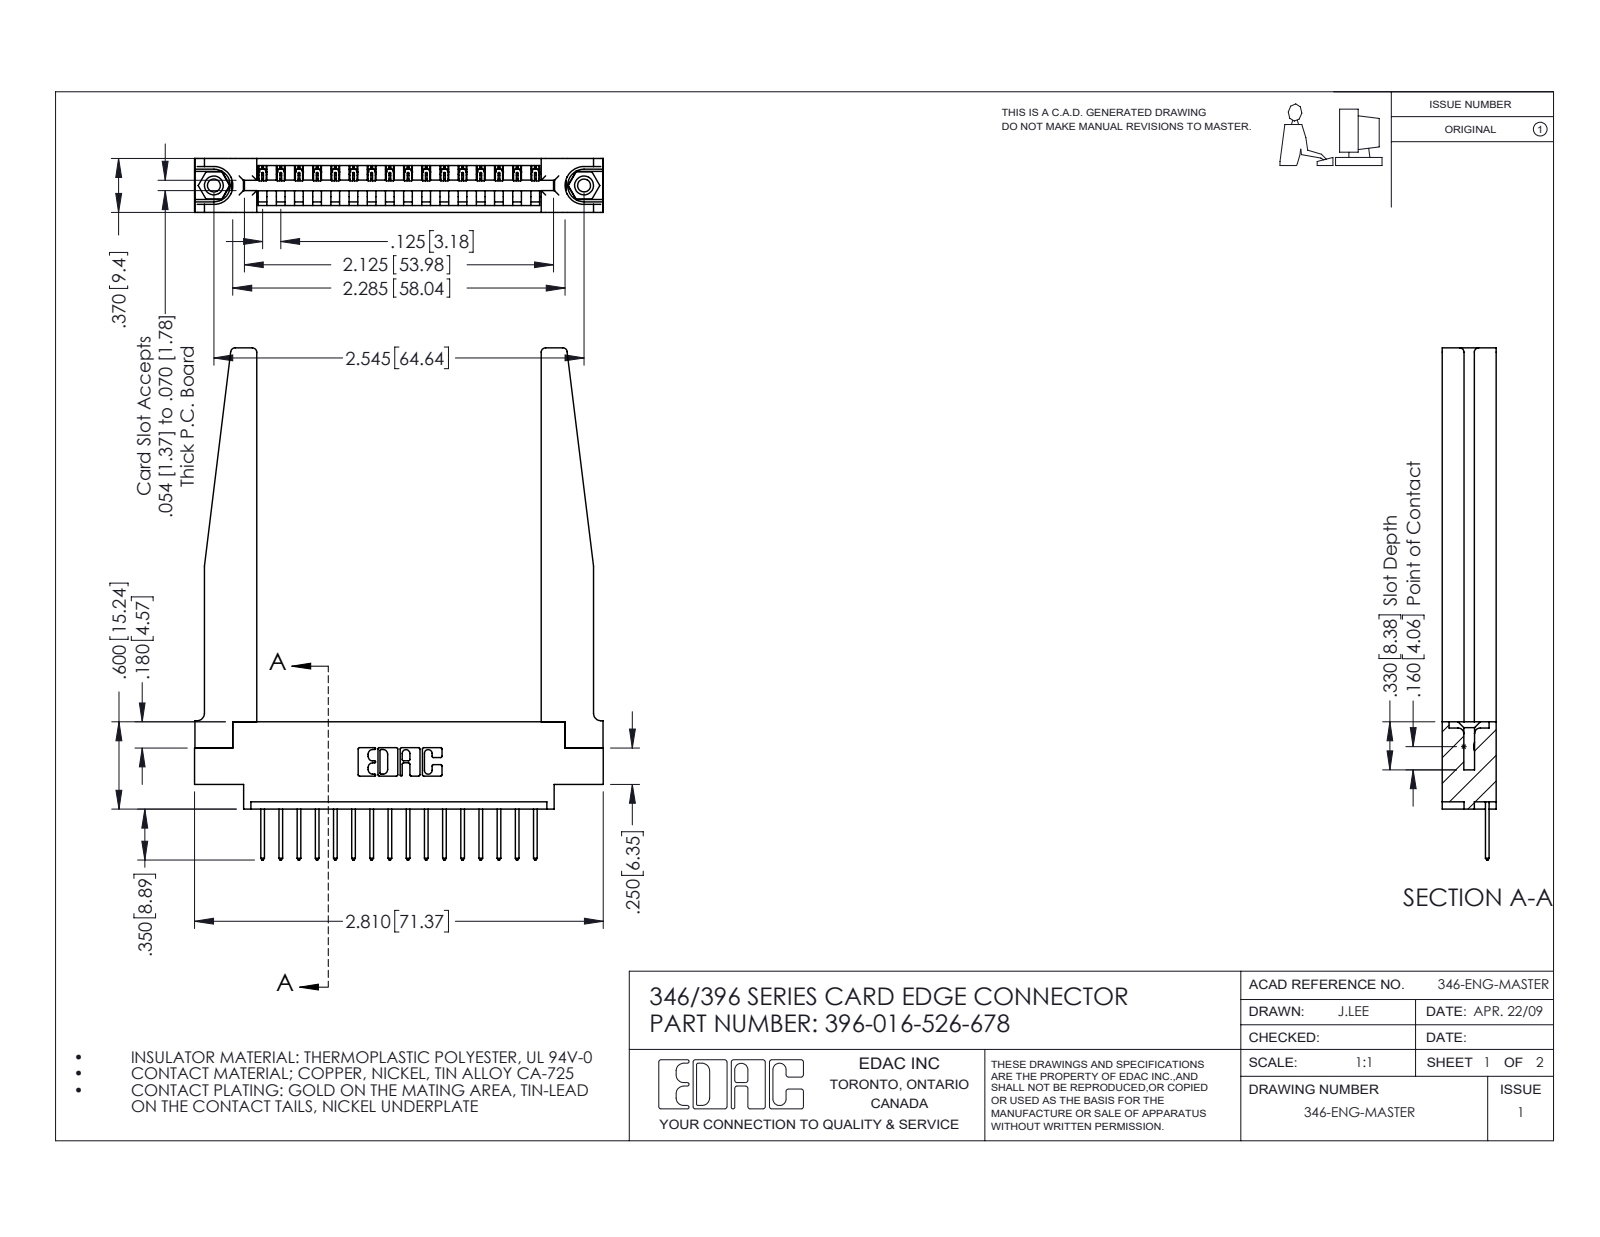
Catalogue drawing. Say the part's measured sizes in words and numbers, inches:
The part is named "345-292-001_345-293-126; 345-250-001_345-250-001-102; 346 Part_0.170 Offset - 0.156 Dia-TH; 346-220-078_345-220-078 (+1 more)". Its 3-D file was written by "SolidWorks 2016 (CONFIG_CONTROL_DESIGN)". It is 21 solids with 1288 faces: 862 planar, 374 cylindrical and 52 other. Overall it measures 3.52 by 2.81 by 0.37 inches. Its volume is 0.817 cubic inches and its surface area 22.49 square inches. Round holes: 2 of diameter 0.089, 2 of diameter 0.125, 2 of diameter 0.156, 1 of diameter 0.064. Round bosses or shafts: 2 of diameter 0.155. Partial cylindrical surfaces (rounded edges, fillets, slot ends): 32 of radius 0.006, 32 of radius 0.01, 22 of radius 0.01, 8 of radius 0.03, 6 of radius 0.007, 6 of radius 0.031, 3 of radius 0.026, 2 of radius 0.031. The main face-to-face distances are 0.37, 0.072, 0.15, 0.048, 0.322, 0.148, 0.25, 0.102, 0.22, 0.173. The hole center spacings are 0.246, 2.338, 2.545.
